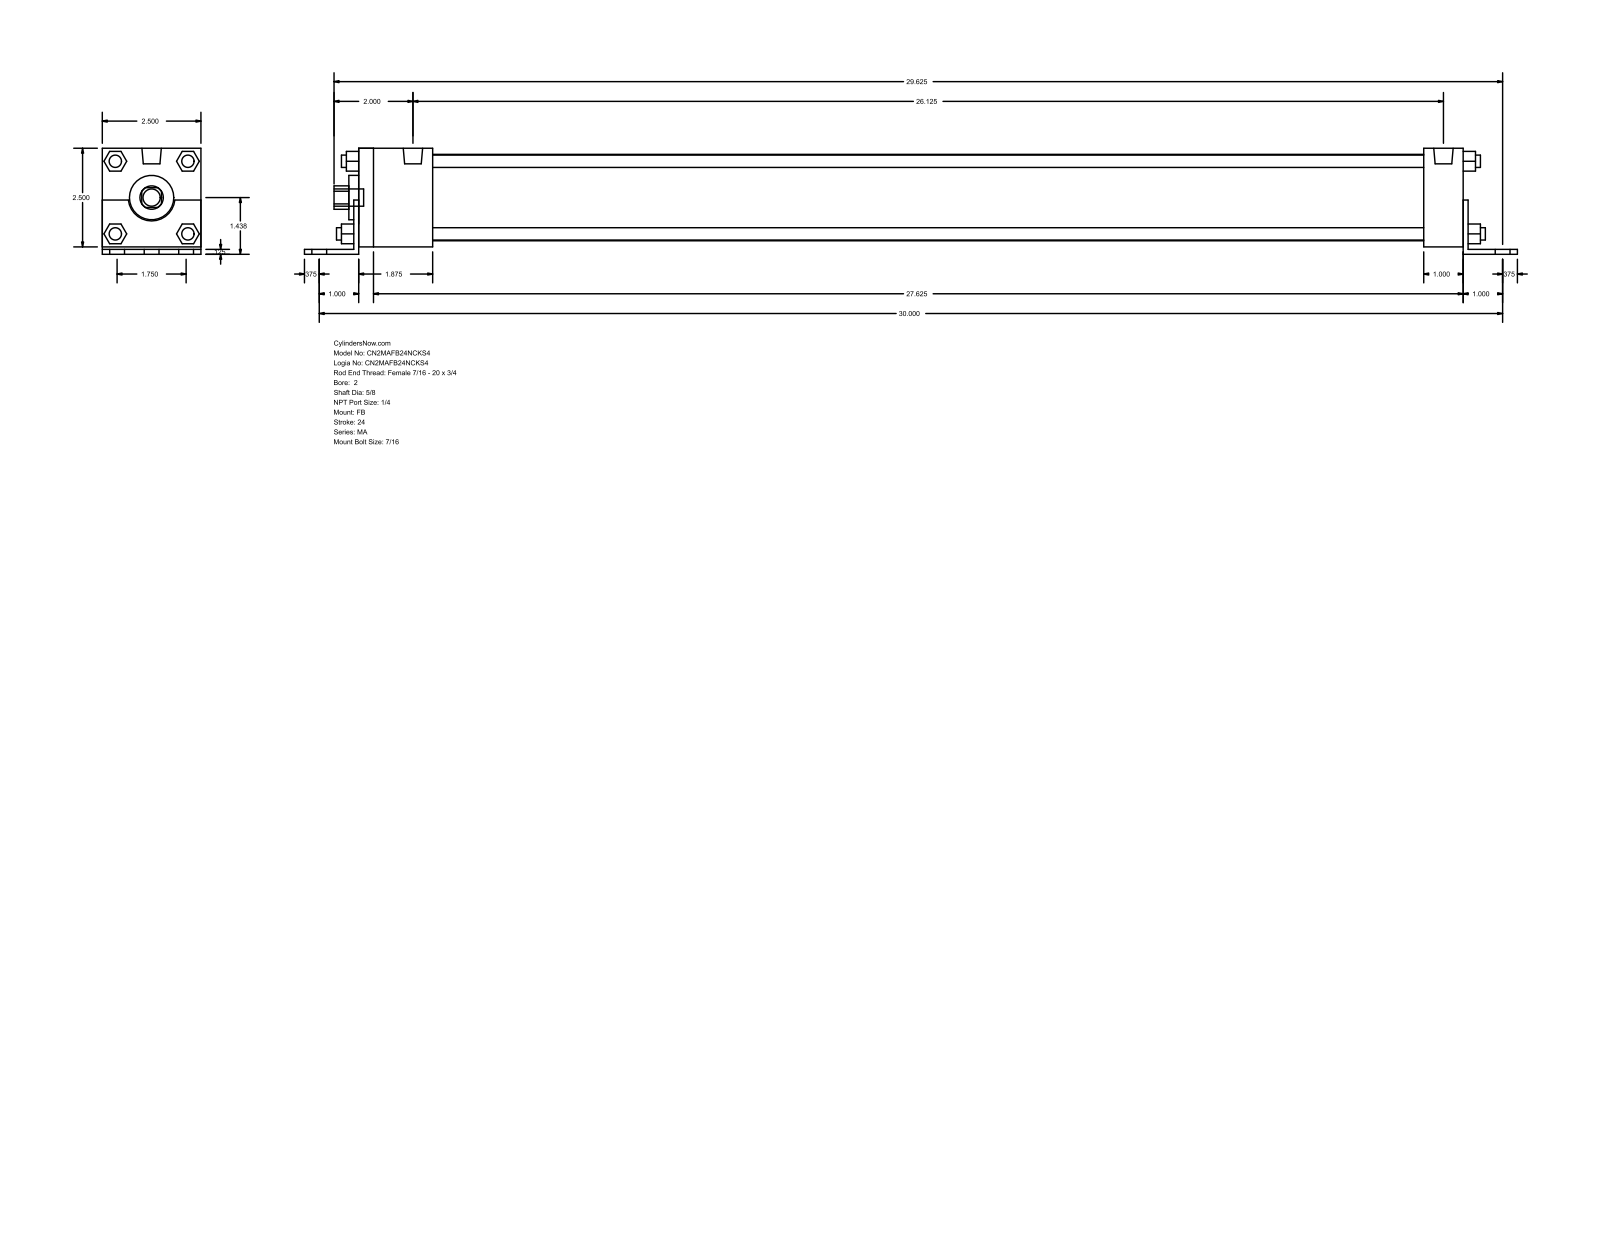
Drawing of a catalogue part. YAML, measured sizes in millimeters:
part_name: "MA_FB__0200_0.625"
step_written_by: "GSSL Pune (CONFIG_CONTROL_DESIGN)"
units: millimeters
bodies: {solids: 0, faces: 140, planar: 105, cylindrical: 35, other: 0}
overall_size: [781.05, 68.26, 63.5]
round_holes:
  - {diameter: 15.88, count: 1}
  - {diameter: 28.57, count: 1}
  - {diameter: 55.63, count: 1}
round_bosses_or_shafts:
  - {diameter: 7.94, count: 8}
  - {diameter: 11.11, count: 7}
  - {diameter: 12.49, count: 2}
partial_cylinders:
  - {radius: 7.54, count: 1}
  - {radius: 15.05, count: 1}
face_to_face_distances: [63.5, 3.17, 4.76, 68.26, 1.59, 65.09, 711.2, 717.55, 3.18, 714.37]
